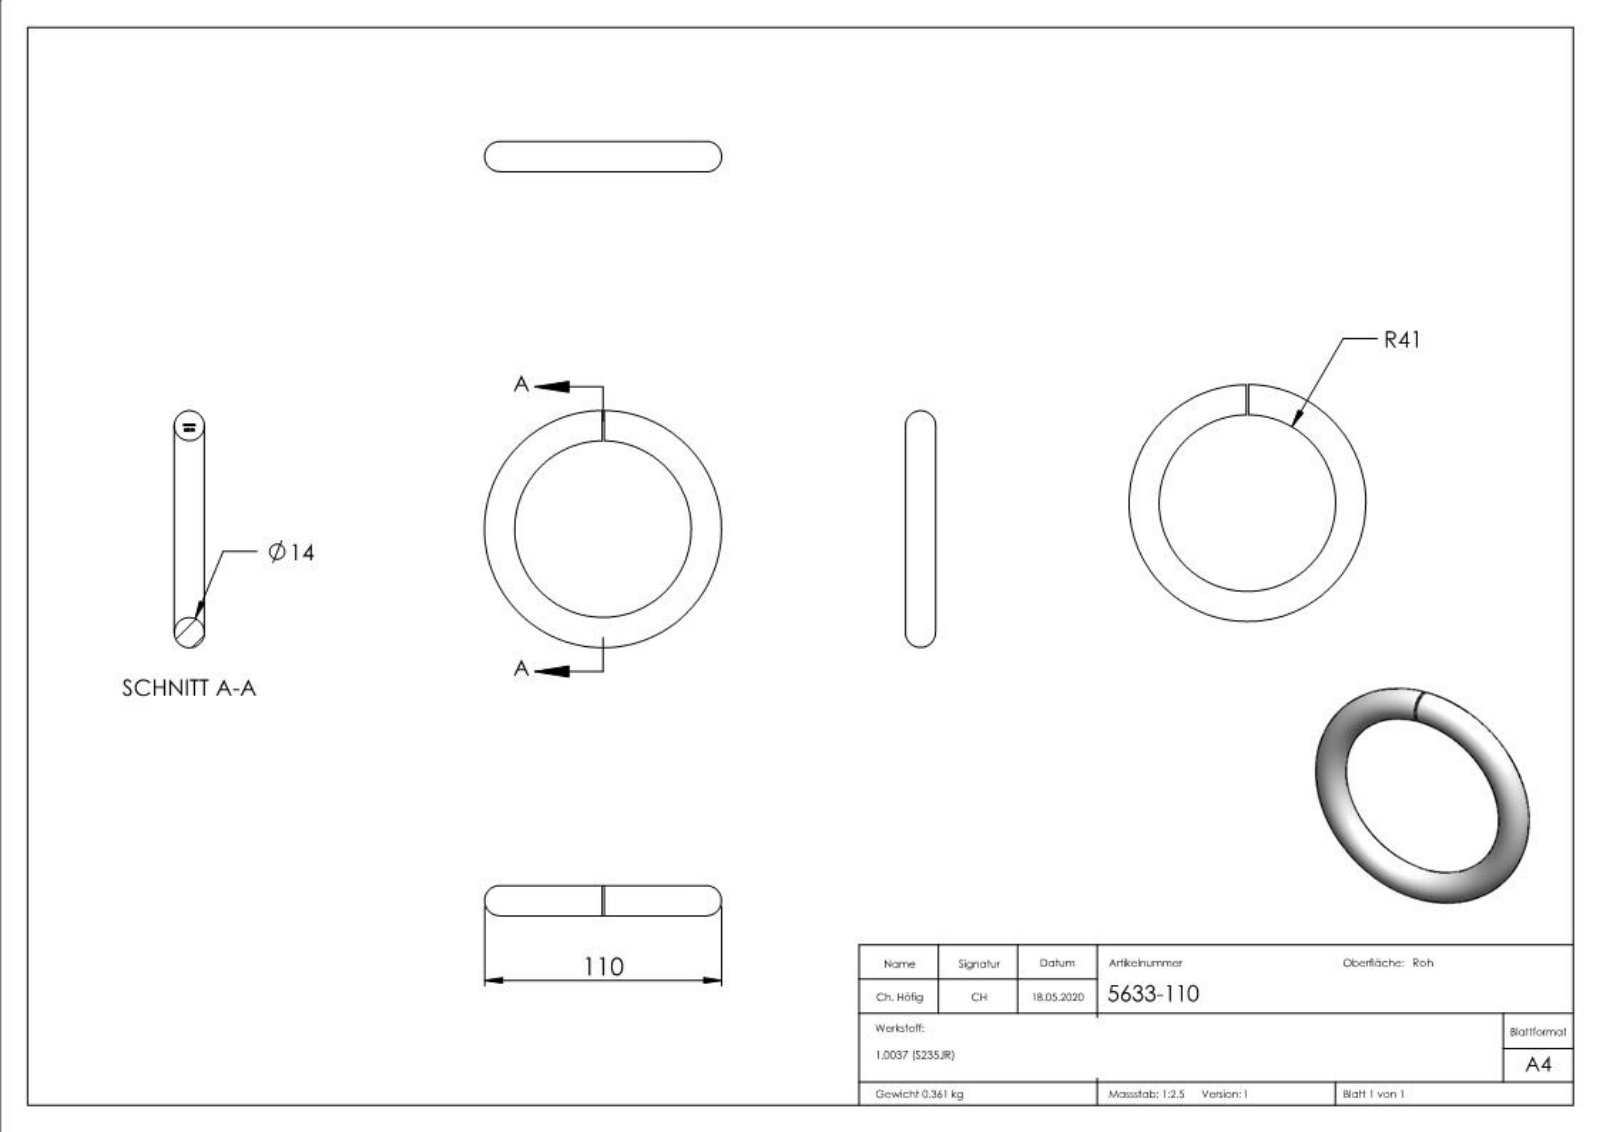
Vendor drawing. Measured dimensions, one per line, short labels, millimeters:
name: 5633-110
written by: SolidWorks 2015 (CONFIG_CONTROL_DESIGN)
unit: mm
bodies: 1 solid, 211 faces (108 planar, 0 cylindrical, 103 other)
size: 110 × 110 × 14
volume: 46 254 mm³; area: 13 555 mm²
face distances: 1, 1.5, 0.5, 1.78, 0.83, 2.45, 2.12, 0.99, 0.61, 2.73
